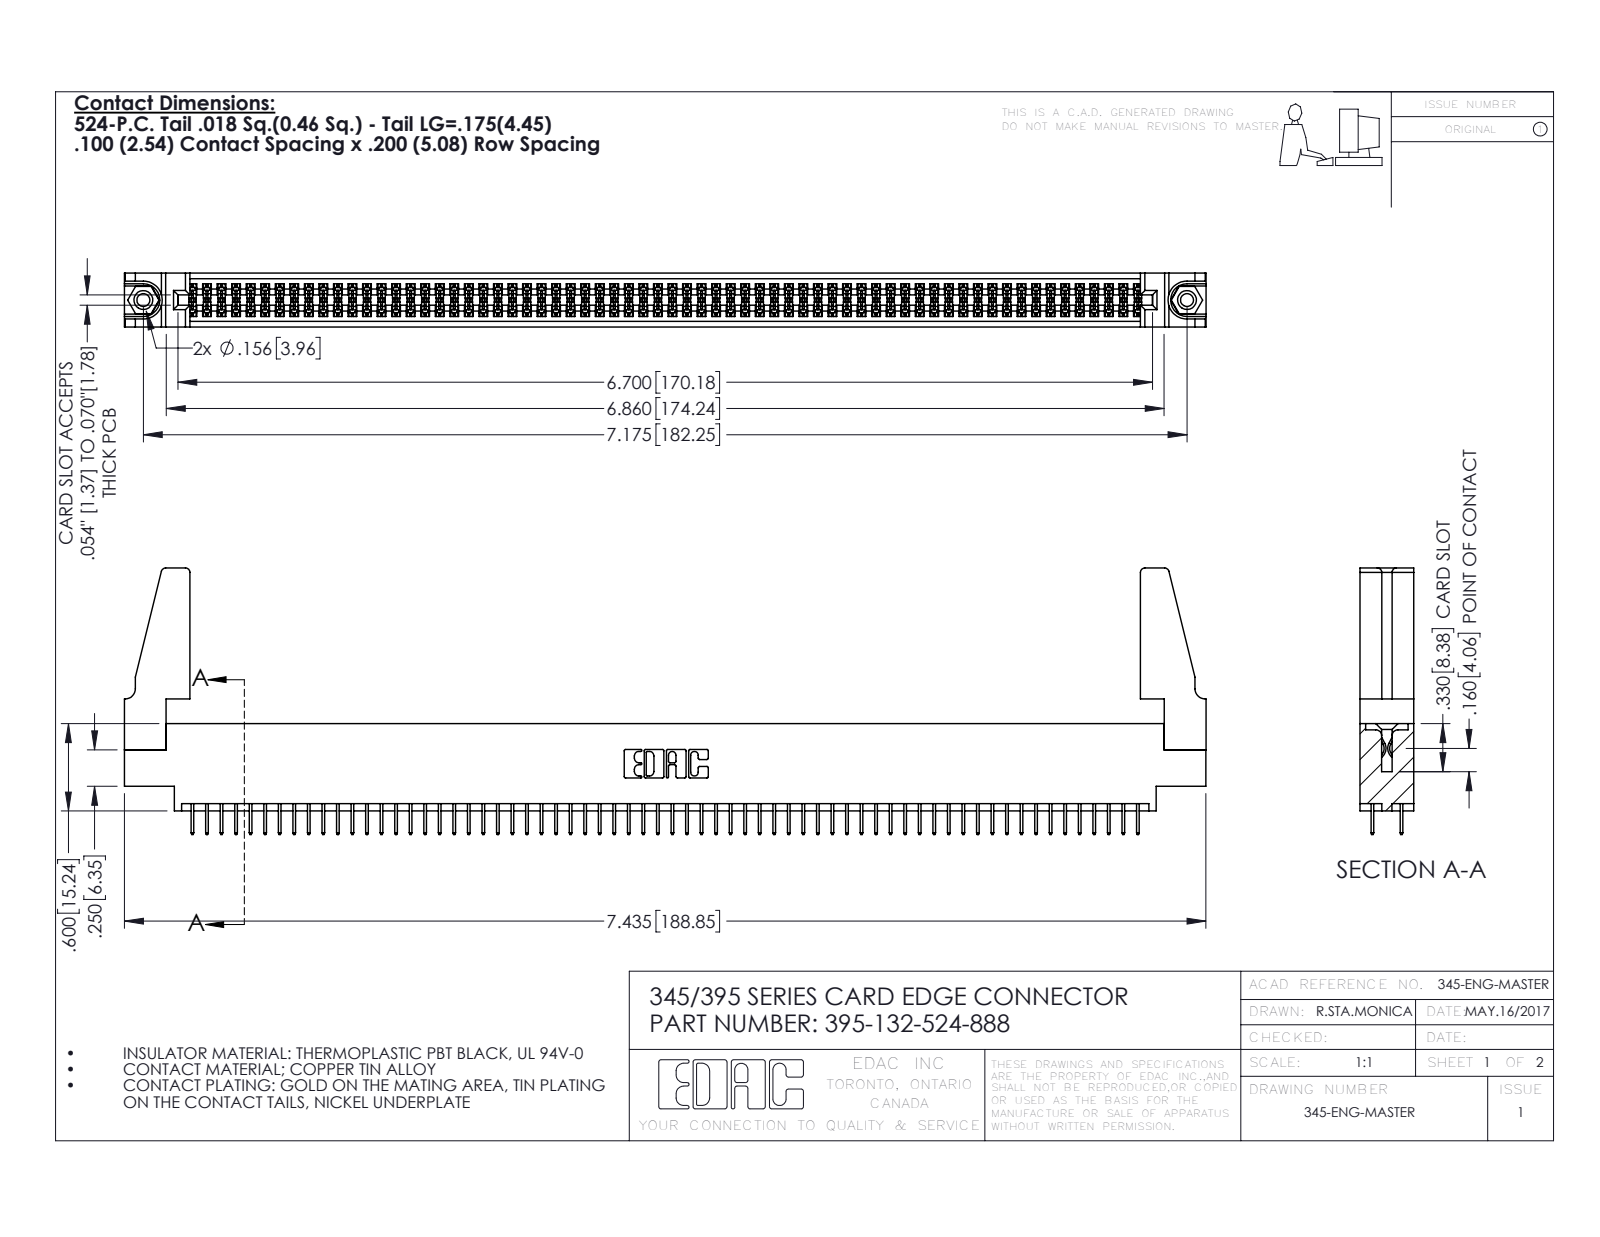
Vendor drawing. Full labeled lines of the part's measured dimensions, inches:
Part name (STEP PRODUCT): 345-250-001_345-250-001-102; 345 Part_0.170 Offset - 0.156 Dia-TH; 345-292-001_345-293-124; 345-220-078_345-220-088 (+1 more)
STEP written by: SolidWorks 2016 (CONFIG_CONTROL_DESIGN)
Units: inches
Bodies: 137 solids, 7382 faces (5304 planar, 2062 cylindrical, 16 other)
Overall size (bounding box): 7.436 × 1.832 × 0.37
Volume: 1.313 in³ · Surface area: 46.79 in²
Round holes (diameter × count): ⌀0.089 ×2, ⌀0.125 ×2, ⌀0.156 ×2, ⌀0.064 ×1
Round bosses / shafts (diameter × count): ⌀0.155 ×2
Partial cylindrical surfaces — rounded edges, fillets, slot ends (radius × count): R0.006 ×198, R0.01 ×22, R0.03 ×8, R0.007 ×6, R0.031 ×6, R0.026 ×3, R0.014 ×2, R0.019 ×2
Main face-to-face distances: 0.072, 0.298, 0.37, 0.2, 0.098, 0.272, 0.025, 0.225, 0.072, 0.175
Hole centre spacings: 0.27, 6.939, 7.175
